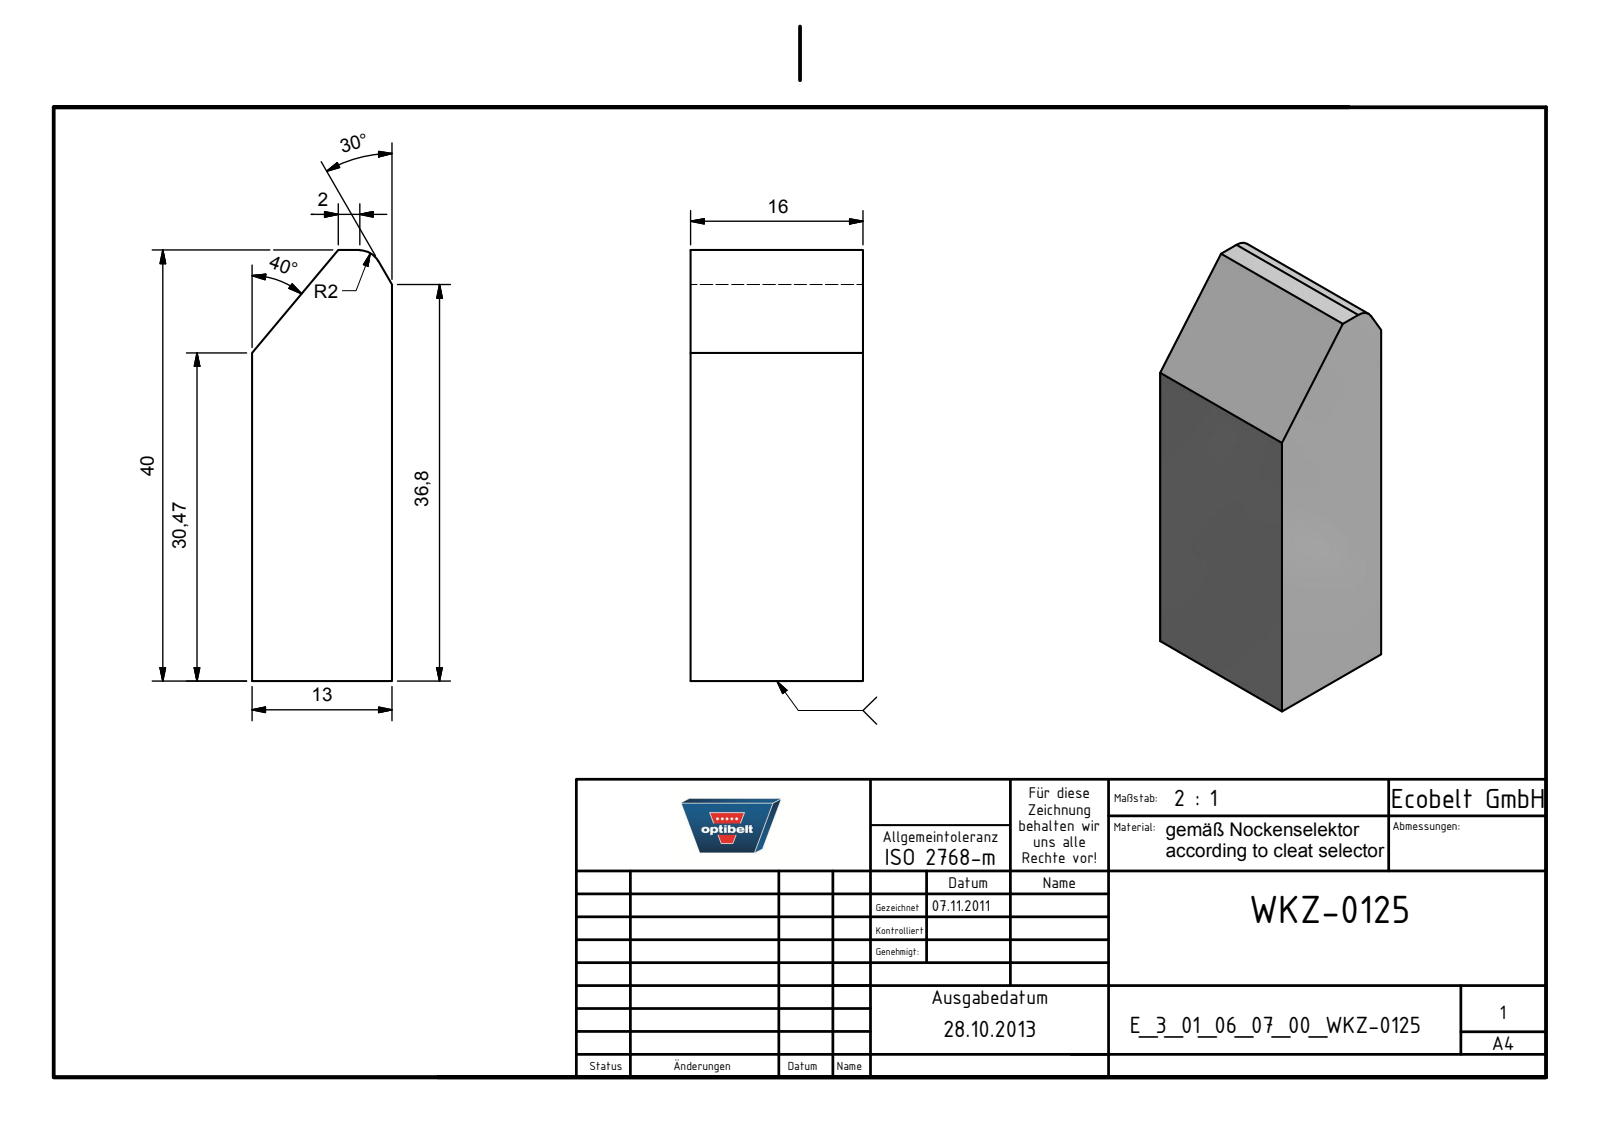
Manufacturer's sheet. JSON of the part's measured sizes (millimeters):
{"part_name": "E_3_01_06_07_00_WKZ-0125", "step_written_by": "Autodesk Inventor 2025 (AUTOMOTIVE_DESIGN)", "units": "millimeters", "bodies": {"solids": 1, "faces": 9, "planar": 8, "cylindrical": 1, "other": 0}, "overall_size": [40, 16, 13], "volume_mm3": 7660, "surface_area_mm2": 2547, "partial_cylinders_radius": [[2, 1]], "face_to_face_distances": [13, 16, 40]}
